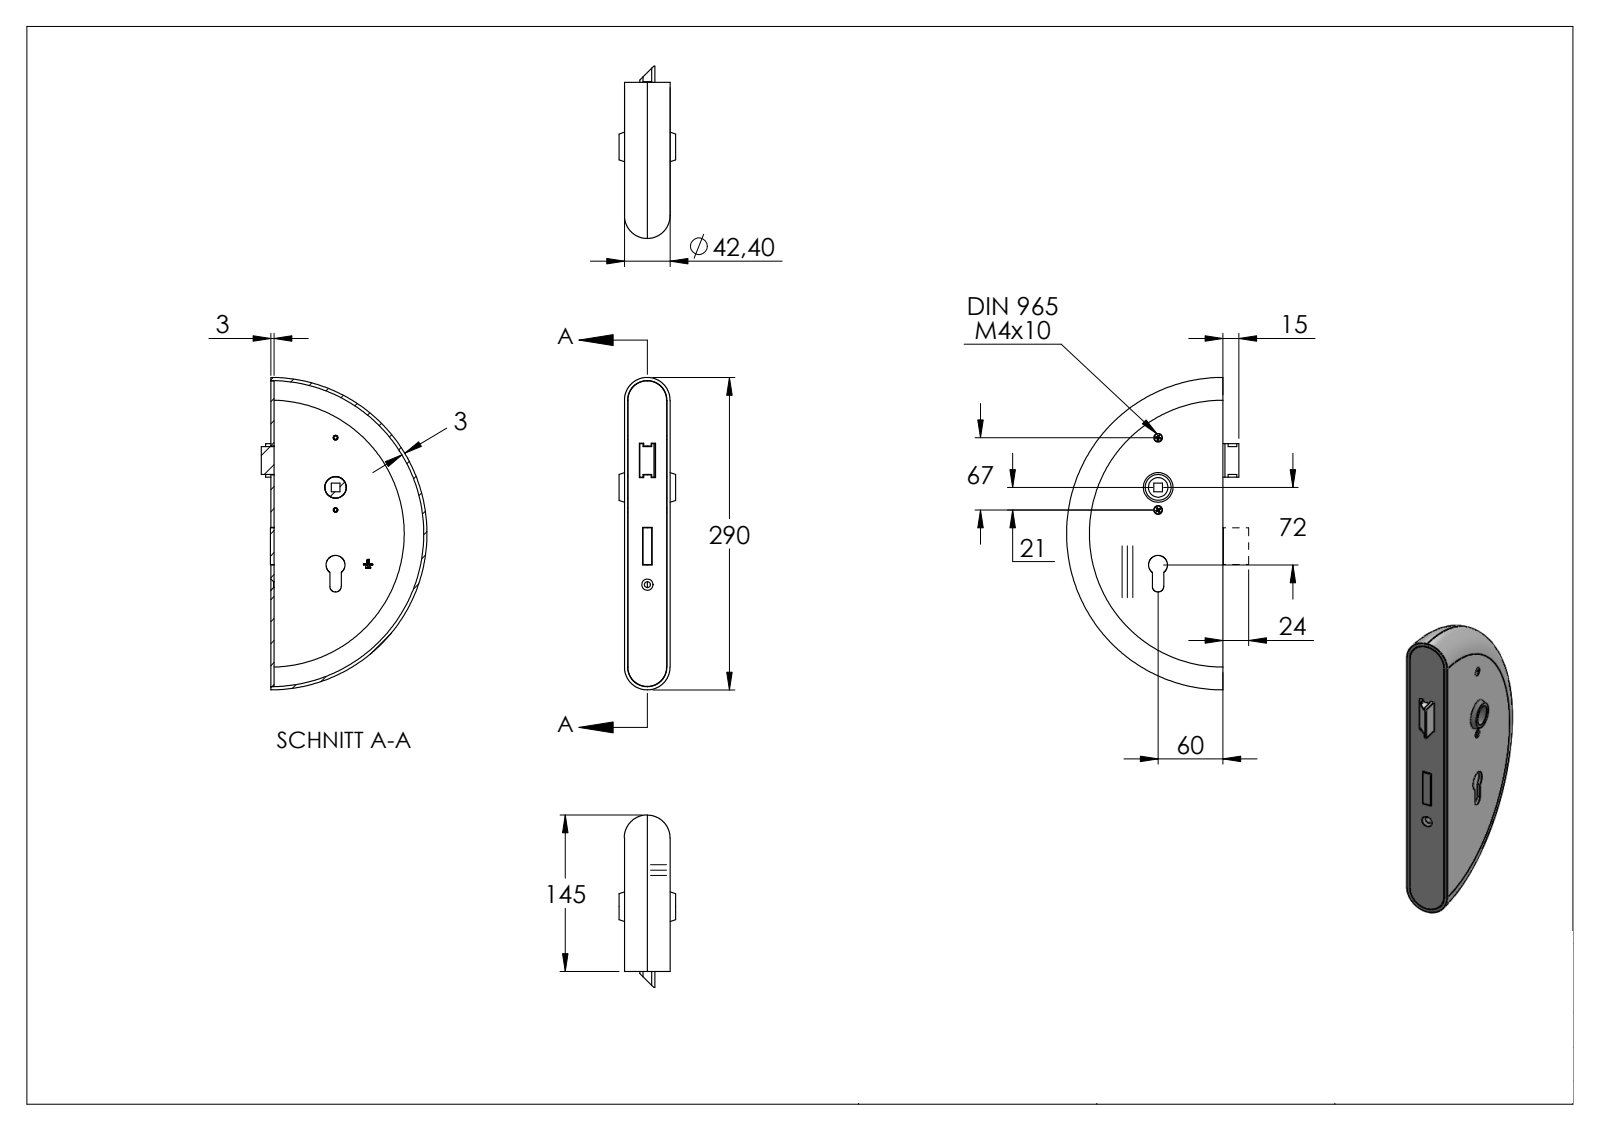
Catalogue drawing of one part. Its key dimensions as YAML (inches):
part_name: "DIN 965; 14530 Teil1; 14530 Teil2; 14530 Teil2_14530 Teil2 (+3 more)"
step_written_by: "SolidWorks 2018 (CONFIG_CONTROL_DESIGN)"
units: inches
bodies: {solids: 11, faces: 454, planar: 243, cylindrical: 66, other: 145}
overall_size: [11.417, 6.299, 2.063]
volume: 16.15
surface_area: 280.5
round_holes:
  - {diameter: 0.169, count: 2}
  - {diameter: 0.315, count: 2}
  - {diameter: 0.217, count: 1}
  - {diameter: 0.693, count: 1}
  - {diameter: 0.715, count: 1}
  - {diameter: 0.787, count: 1}
round_bosses_or_shafts:
  - {diameter: 0.283, count: 2}
  - {diameter: 0.157, count: 2}
  - {diameter: 0.142, count: 2}
  - {diameter: 0.78, count: 1}
partial_cylinders:
  - {radius: 0.709, count: 2}
  - {radius: 0.207, count: 1}
face_to_face_distances: [0.118, 1.551, 1.433, 1.669, 0.126, 1.543, 1.425, 0.992, 0.559, 0.433]
hole_center_spacings: [0.827, 1.811, 2.008, 2.638, 2.835, 4.646]
